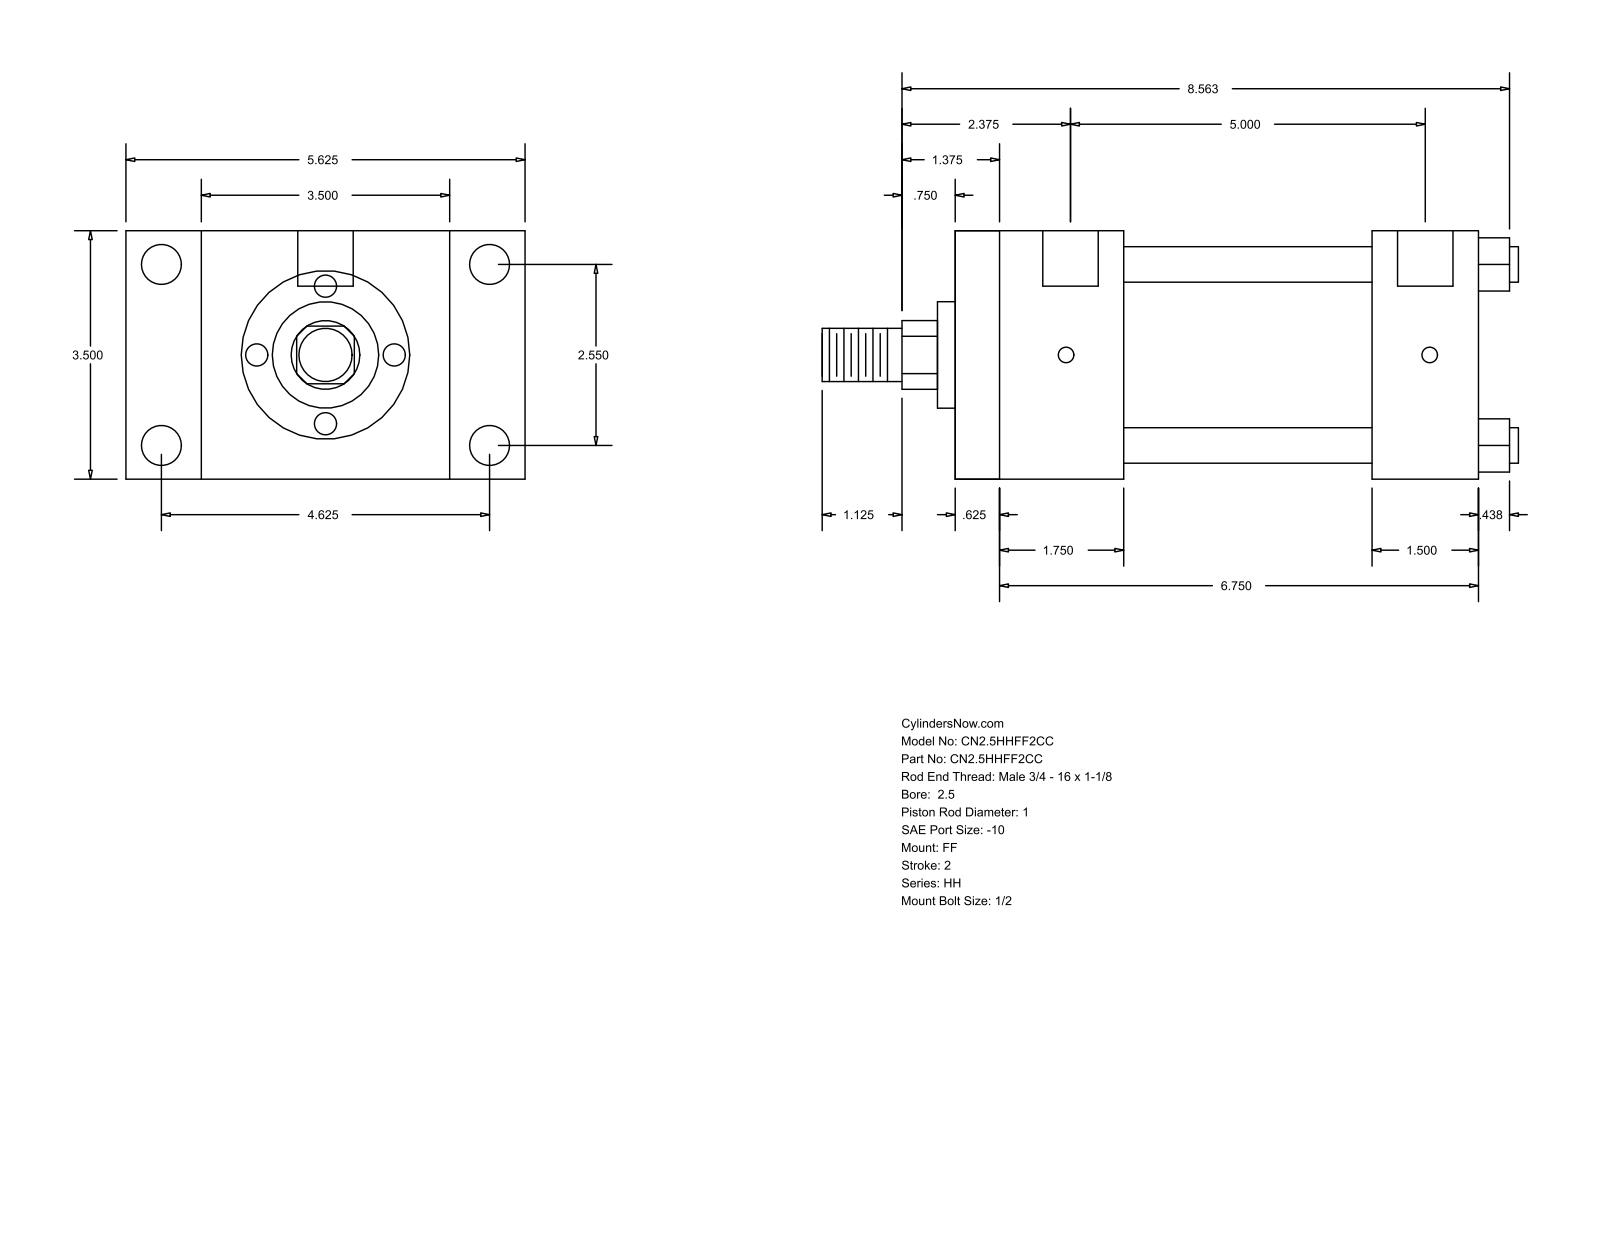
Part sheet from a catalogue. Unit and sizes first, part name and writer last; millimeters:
Units: millimetres
Overall size (bounding box): 249.24 × 142.88 × 88.9
Round holes (diameter × count): ⌀5.56 ×4, ⌀14.3 ×4, ⌀19.84 ×2
Round bosses / shafts (diameter × count): ⌀12.7 ×4, ⌀73.03 ×1, ⌀38.1 ×1, ⌀25.4 ×1, ⌀19.05 ×1
Partial cylindrical surfaces — rounded edges, fillets, slot ends (radius × count): R12.29 ×1
Main face-to-face distances: 88.9, 187.33, 15.87, 171.46, 38.1, 60.33, 44.46, 127, 149.23, 133.36
Hole centre spacings: 1.59, 64.76, 117.48, 128.58, 130.17, 134.15, 126.99
Bodies: 0 solids, 92 faces (64 planar, 28 cylindrical, 0 other)
Part name (STEP PRODUCT): HH_FF__0250_1
STEP written by: GSSL Pune (CONFIG_CONTROL_DESIGN)
